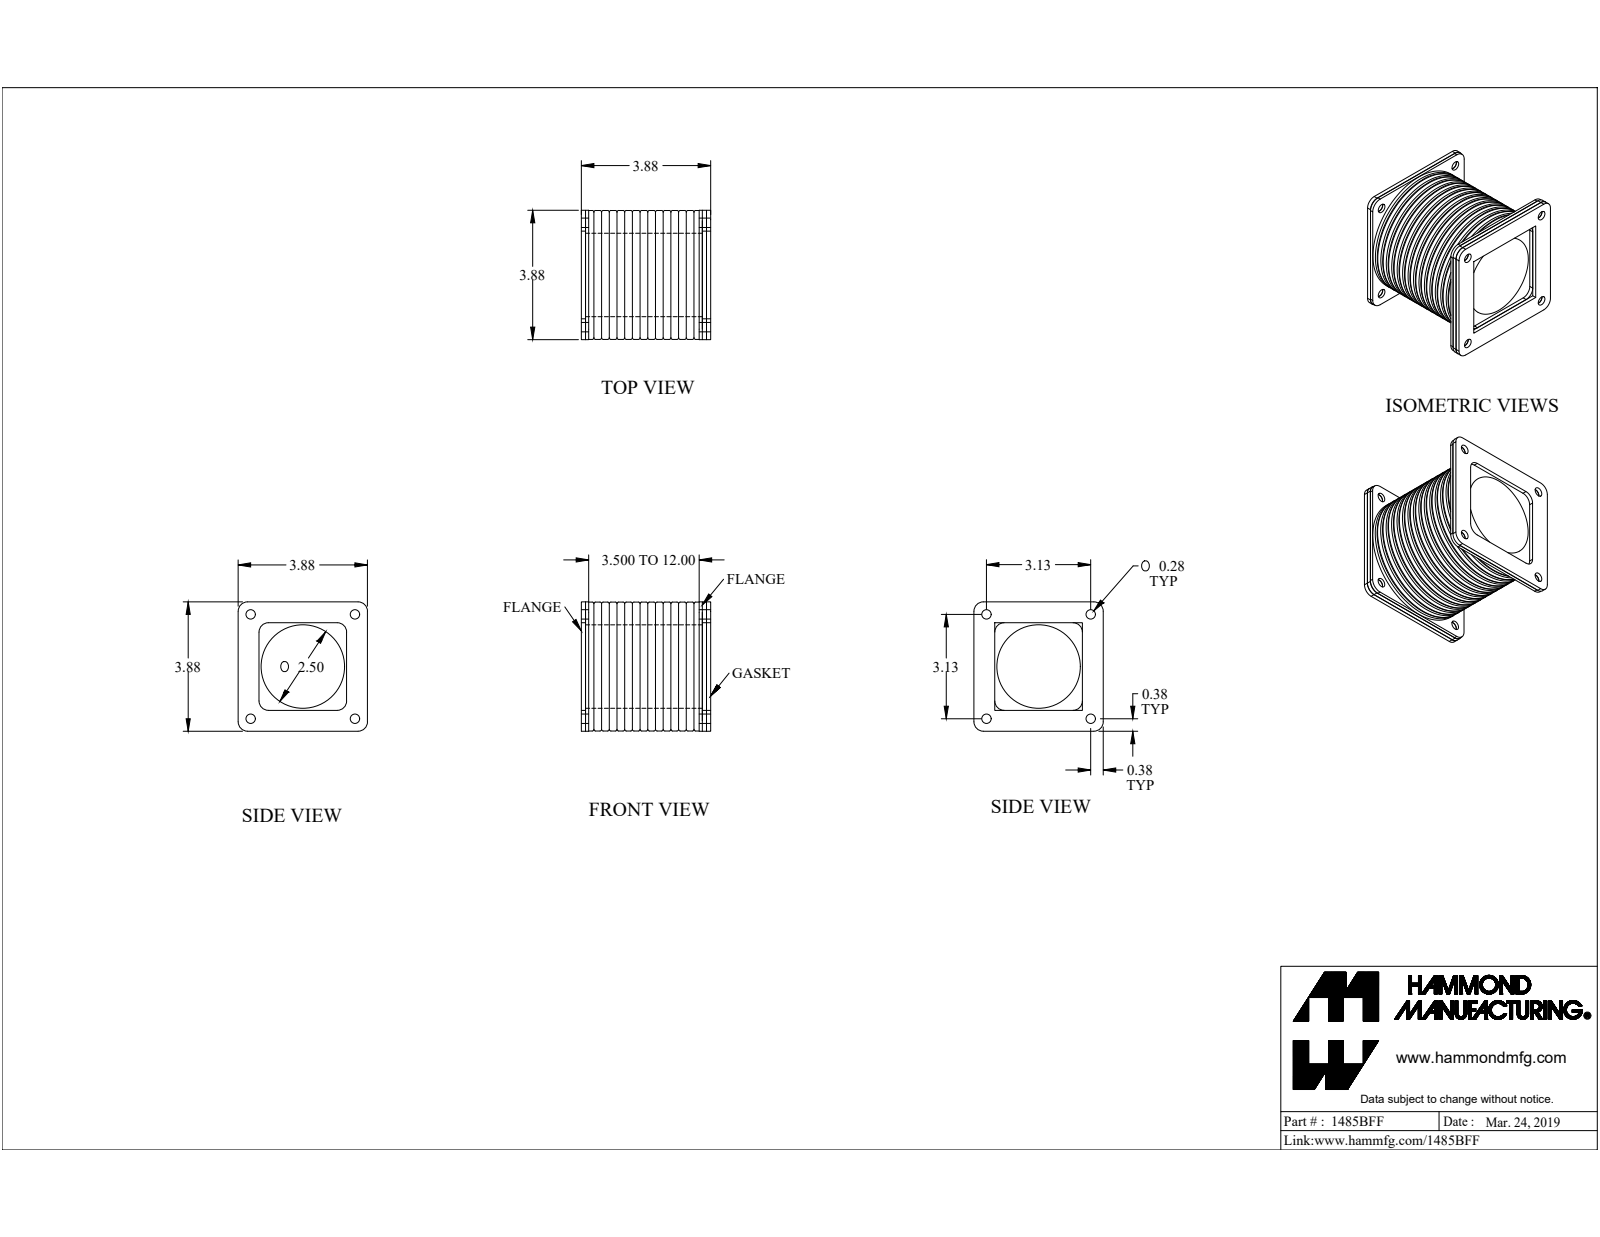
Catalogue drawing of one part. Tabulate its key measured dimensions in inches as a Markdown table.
| quantity | value |
| --- | --- |
| part name | 1485BFF |
| STEP written by | SolidWorks 2019 (CONFIG_CONTROL_DESIGN) |
| units | inches |
| bodies | 4 solids, 134 faces (42 planar, 64 cylindrical, 28 other) |
| overall size | 3.875 × 3.875 × 3.875 |
| volume | 27.14 in³ |
| surface area | 164 in² |
| round holes (diameter × count) | 0.281 × 4, 0.281 × 4, 2.5 × 1 |
| round bosses / shafts (diameter × count) | 3.862 × 1 |
| partial cylindrical surfaces (radius × count) | 0.281 × 8, 0.313 × 4 |
| main face-to-face distances | 0.125, 3.625, 3.5, 3.875, 3.75, 3.75, 0.25, 0.125, 0.22, 3.53 |
| hole center spacings | 2.21, 3.125, 4.42 |
